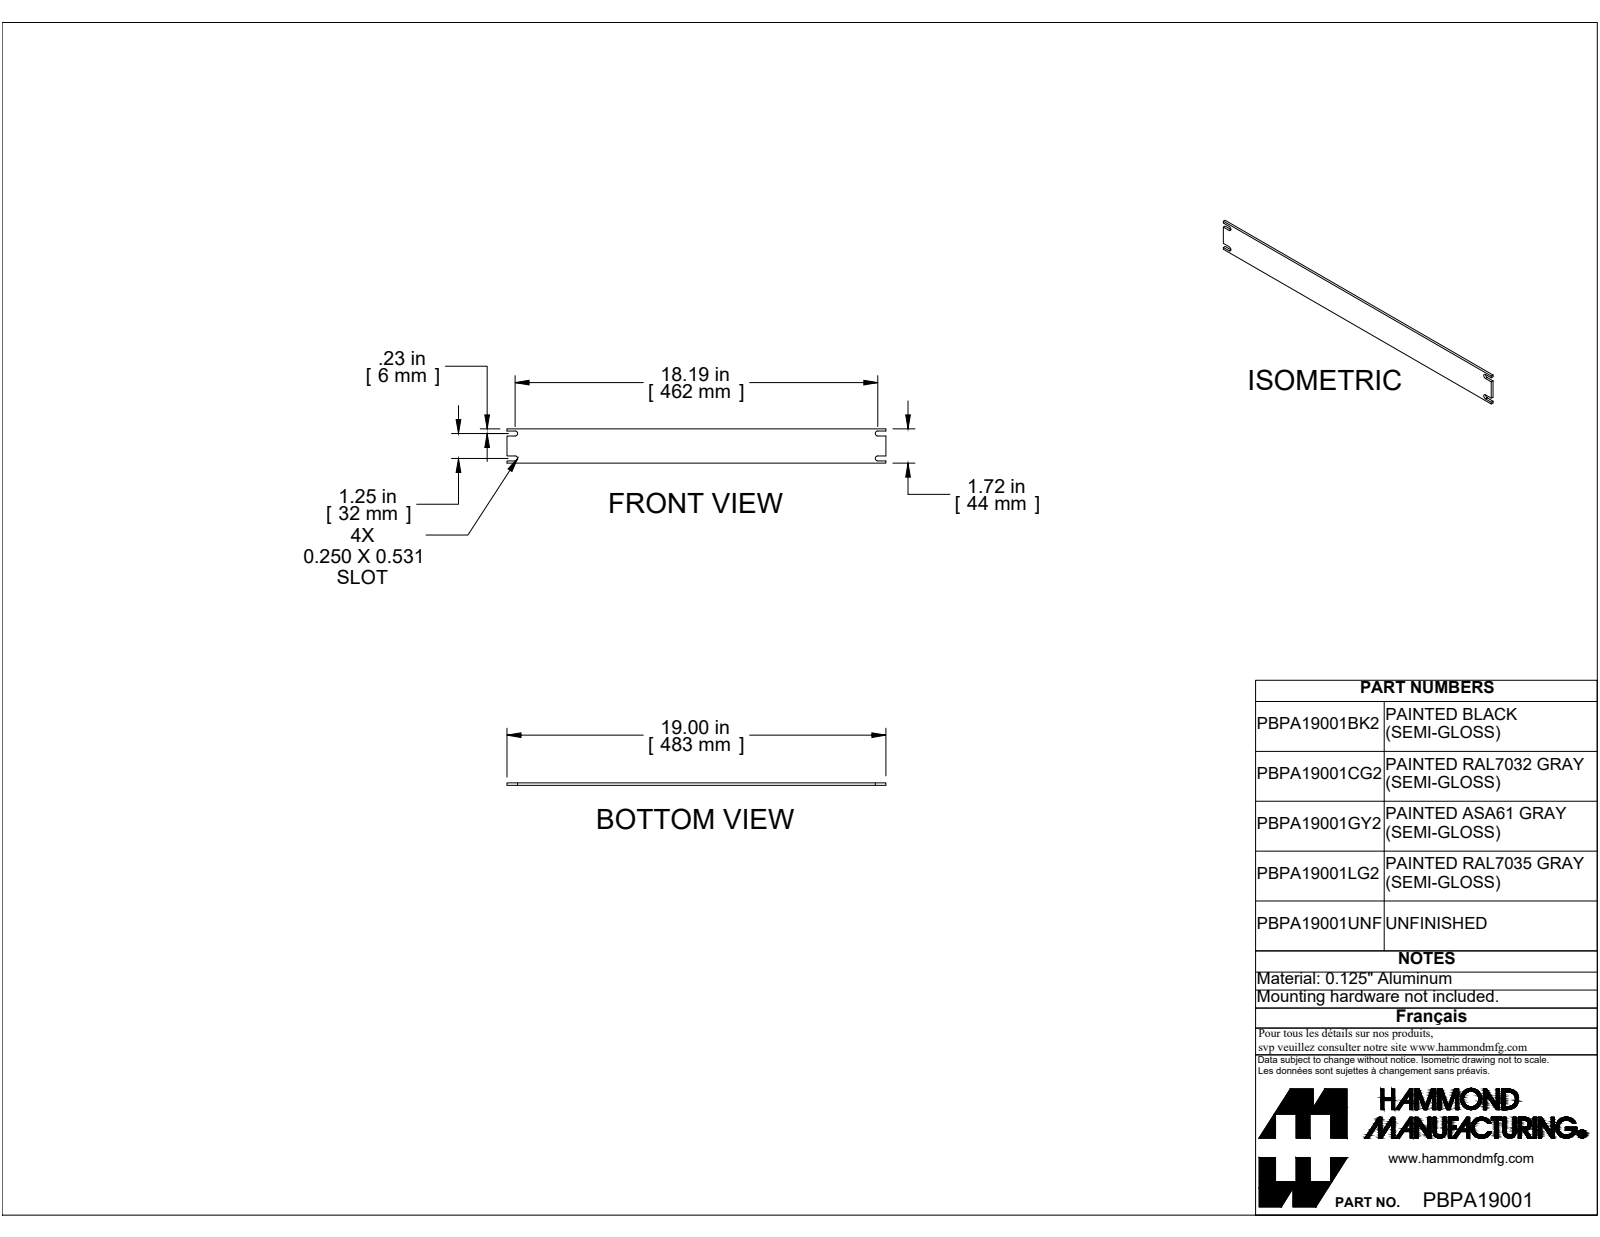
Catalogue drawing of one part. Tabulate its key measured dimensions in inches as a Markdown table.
| quantity | value |
| --- | --- |
| part name | PBPA19001BK2 |
| STEP written by | SolidWorks 2019 (CONFIG_CONTROL_DESIGN) |
| units | inches |
| bodies | 1 solid, 22 faces (18 planar, 4 cylindrical, 0 other) |
| overall size | 19 × 1.718 × 0.125 |
| volume | 4.017 in³ |
| surface area | 69.93 in² |
| partial cylindrical surfaces (radius × count) | 0.125 × 4 |
| main face-to-face distances | 0.125, 1.718, 0.109, 0.359, 1.359, 1.609, 1.25, 0.25, 19, 1.5 |
